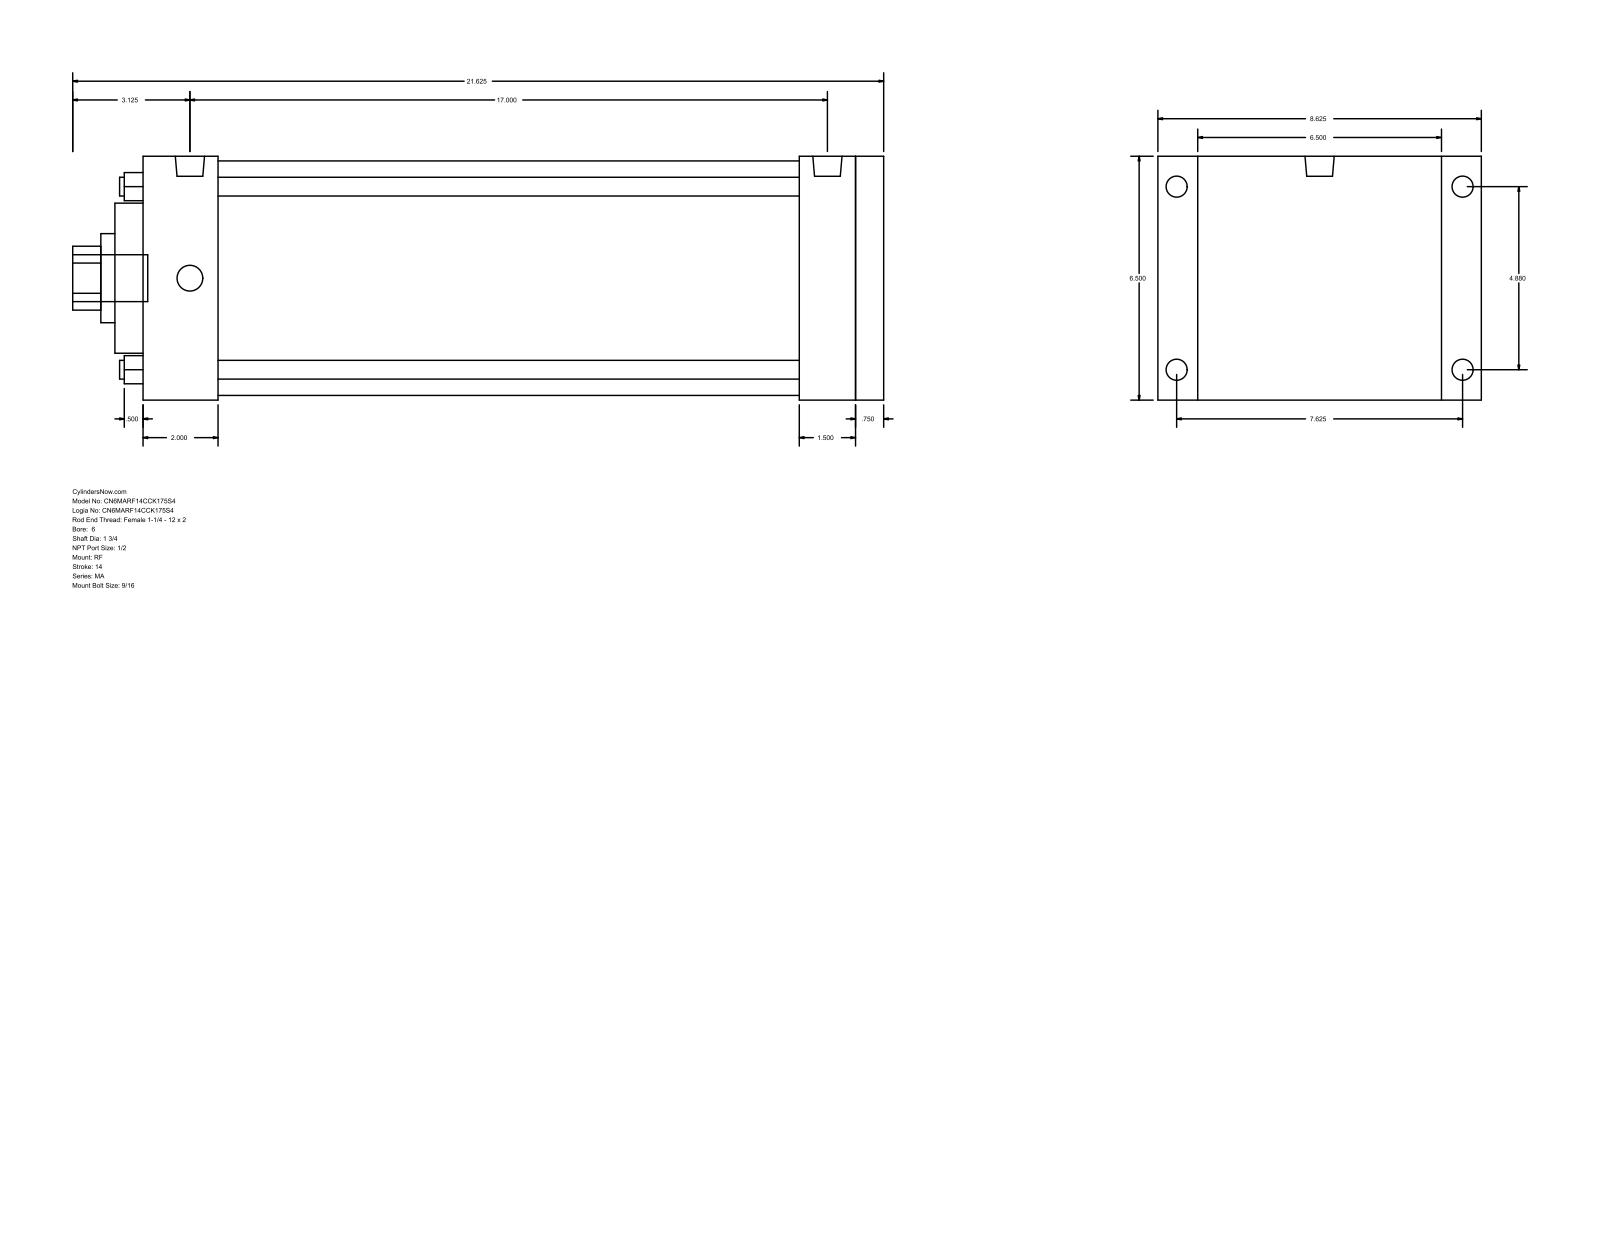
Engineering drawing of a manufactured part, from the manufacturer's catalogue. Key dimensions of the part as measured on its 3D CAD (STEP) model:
Part name (STEP PRODUCT): MA_RF__0600_1.75
STEP written by: GSSL Pune (CONFIG_CONTROL_DESIGN)
Units: millimetres
Bodies: 0 solids, 94 faces (65 planar, 29 cylindrical, 0 other)
Overall size (bounding box): 549.27 × 219.07 × 165.1
Round holes (diameter × count): ⌀12.7 ×4, ⌀44.45 ×1, ⌀60.33 ×1, ⌀101.6 ×1, ⌀158.75 ×1
Round bosses / shafts (diameter × count): ⌀17.46 ×4, ⌀14.29 ×4, ⌀19.77 ×2, ⌀31.75 ×1
Partial cylindrical surfaces — rounded edges, fillets, slot ends (radius × count): R21.63 ×1
Main face-to-face distances: 165.1, 501.65, 19.04, 482.61, 19.05, 50.8, 431.81, 450.85, 444.5, 393.7
Hole centre spacings: 87.65, 123.96, 175.31
